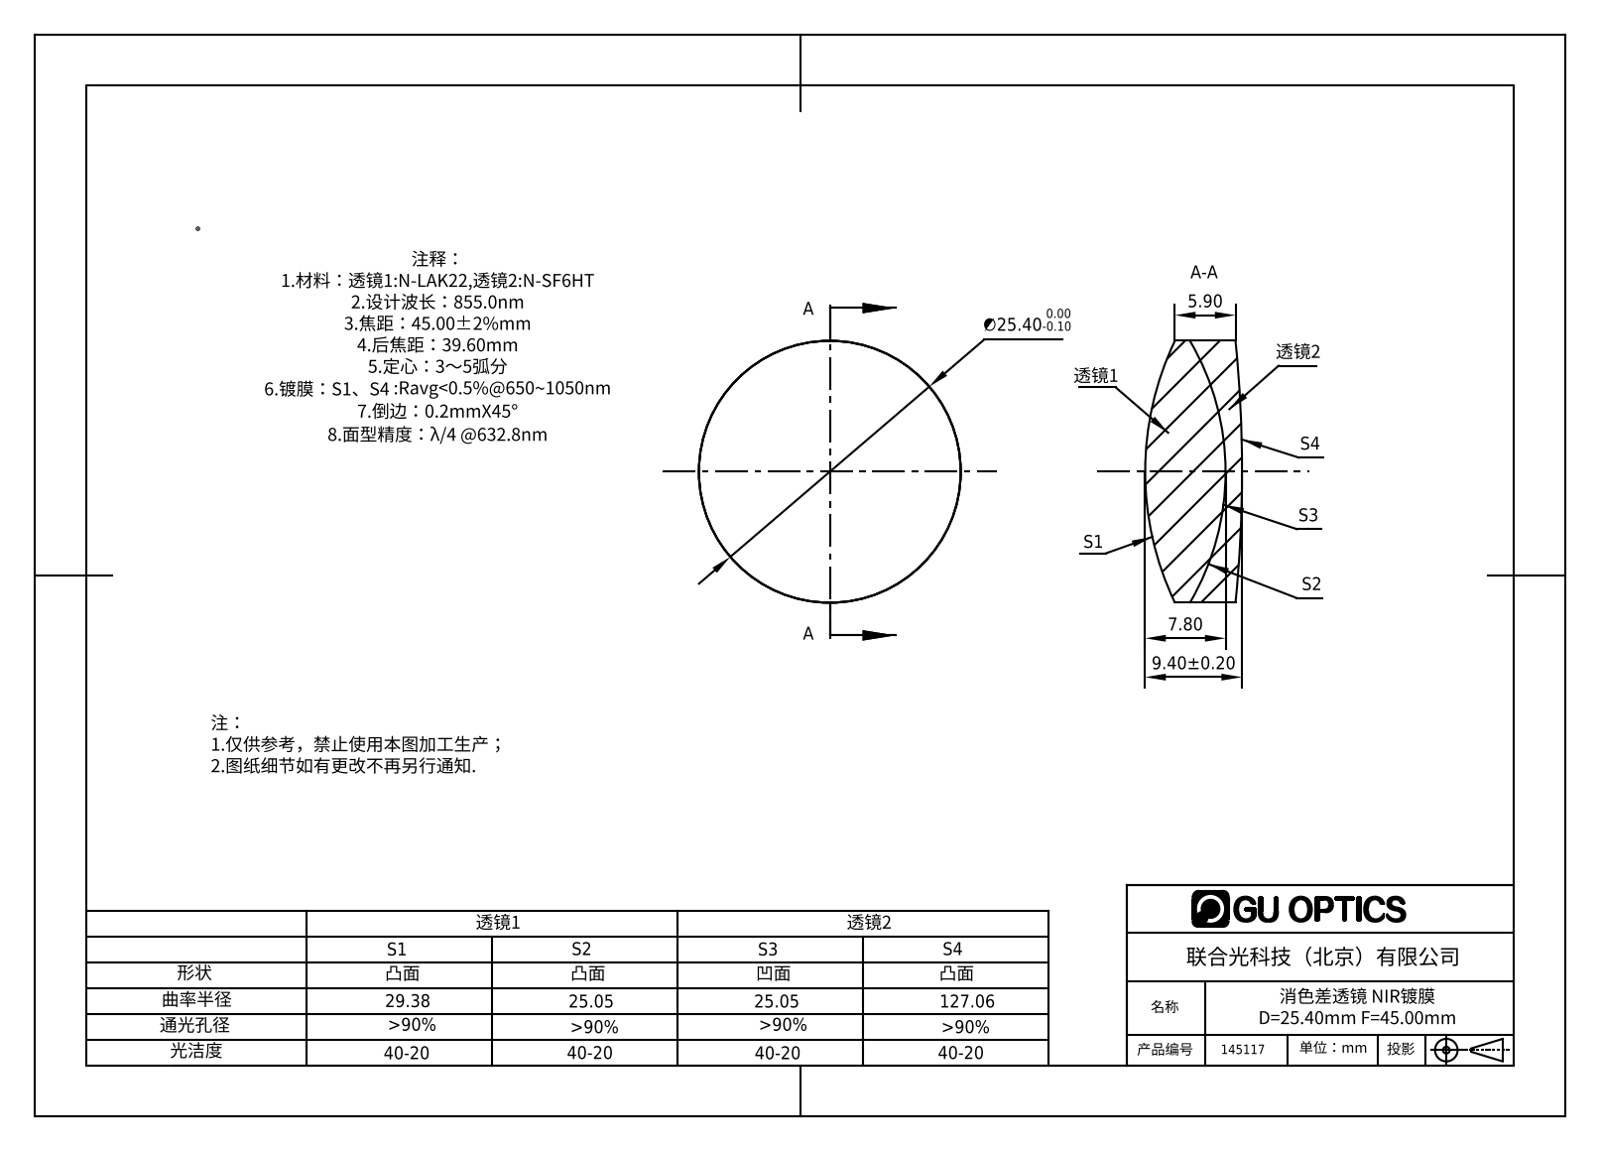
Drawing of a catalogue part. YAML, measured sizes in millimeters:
part_name: "145117"
step_written_by: "SolidWorks 2016 (AUTOMOTIVE_DESIGN)"
units: millimeters
bodies: {solids: 2, faces: 12, planar: 0, cylindrical: 4, other: 8}
overall_size: [25.4, 25.4, 9.4]
volume: 3883
surface_area: 2598
round_bosses_or_shafts:
  - {diameter: 25.4, count: 1}
